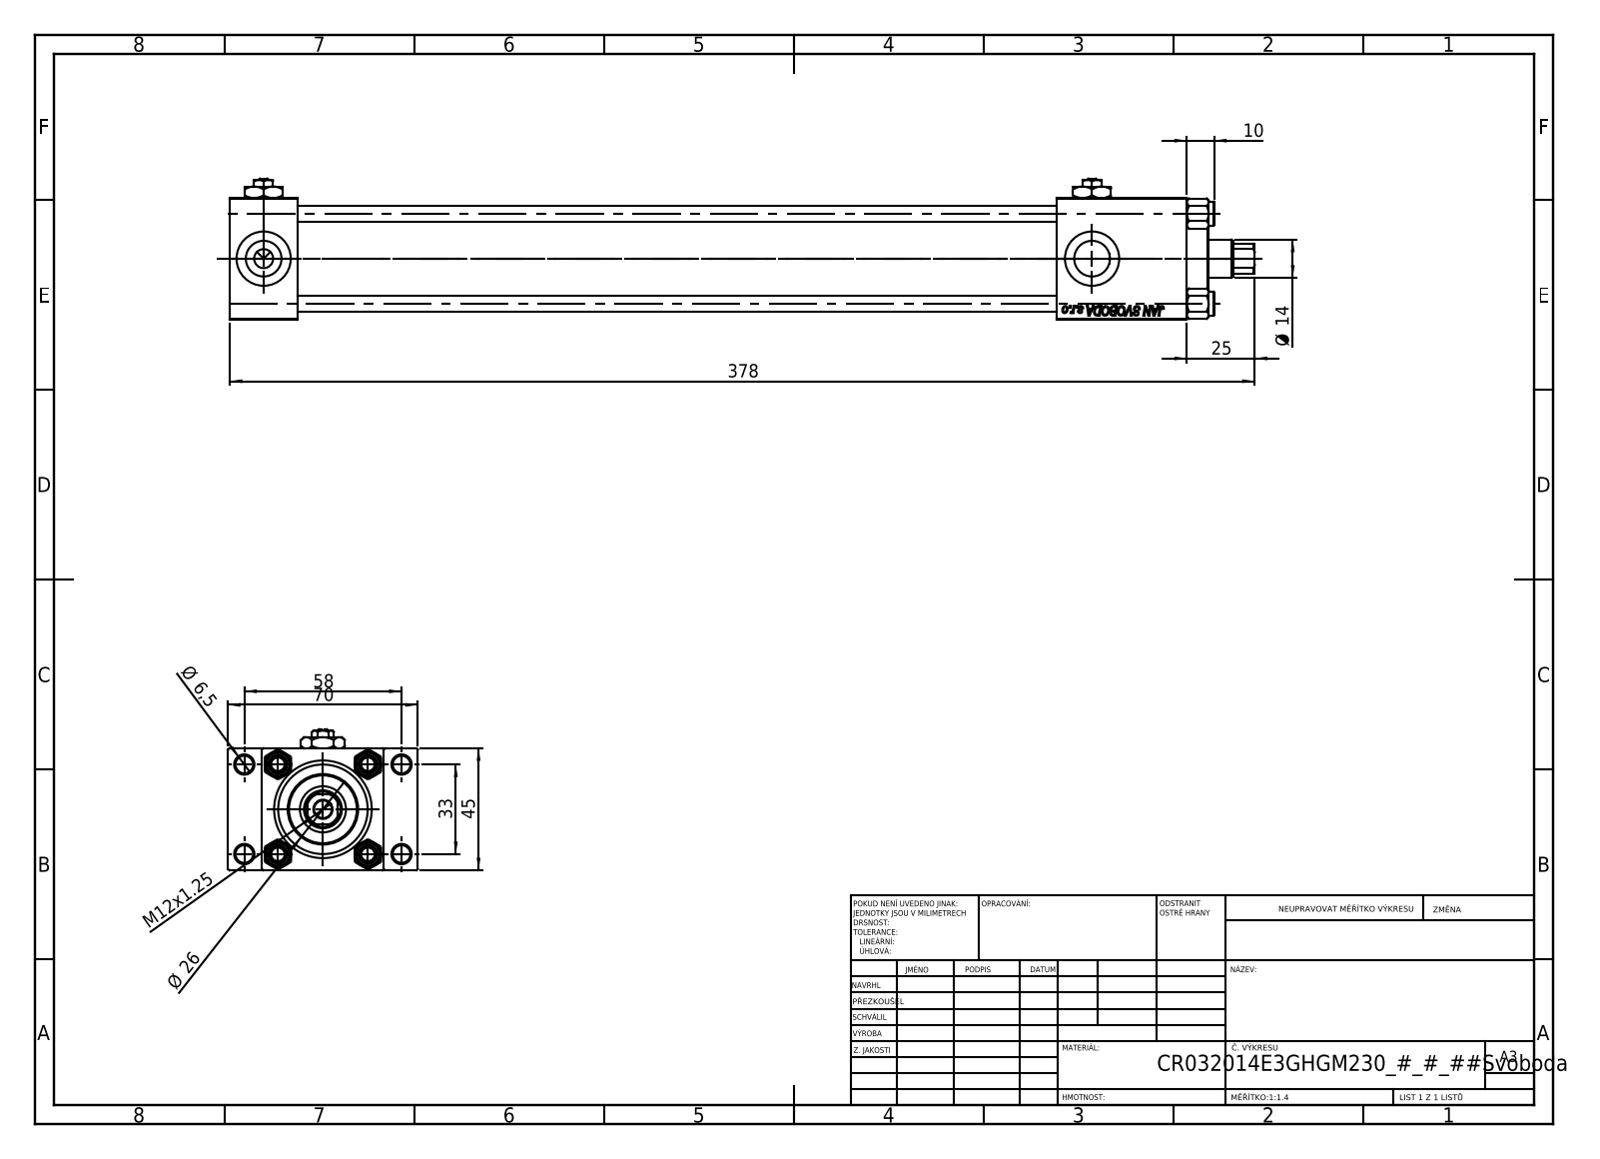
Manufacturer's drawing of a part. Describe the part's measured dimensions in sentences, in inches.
The part is named "V215CR_VCP_E; V215CR_E_Body; V215CR_TYCINKA_E; NUT_M5_E (+2 more)". Its 3-D file was written by "SolidWorks 2019 (CONFIG_CONTROL_DESIGN)". It is 13 solids with 1235 faces: 544 planar, 97 cylindrical and 594 other. Overall it measures 14.882 by 2.756 by 2.047 inches. Its volume is 21.67 cubic inches and its surface area 242.2 square inches. Round holes: 5 of diameter 0.256, 4 of diameter 0.236, 4 of diameter 0.518, 4 of diameter 0.787, 3 of diameter 0.276, 1 of diameter 0.551, 1 of diameter 0.669, 1 of diameter 0.945, 1 of diameter 1.26, 1 of diameter 1.299. Round bosses or shafts: 4 of diameter 0.354, 1 of diameter 1.496, 1 of diameter 1.024. Partial cylindrical surfaces (rounded edges, fillets, slot ends): 1 of radius 0.256. The main face-to-face distances are 1.772, 0.984, 0.492, 2.264, 13.898, 12.913, 12.008, 11.024, 1.89, 12.768. The hole center spacings are 0.488, 0.924, 1.307, 1.314, 1.392, 1.795, 2.219, 1.299.
